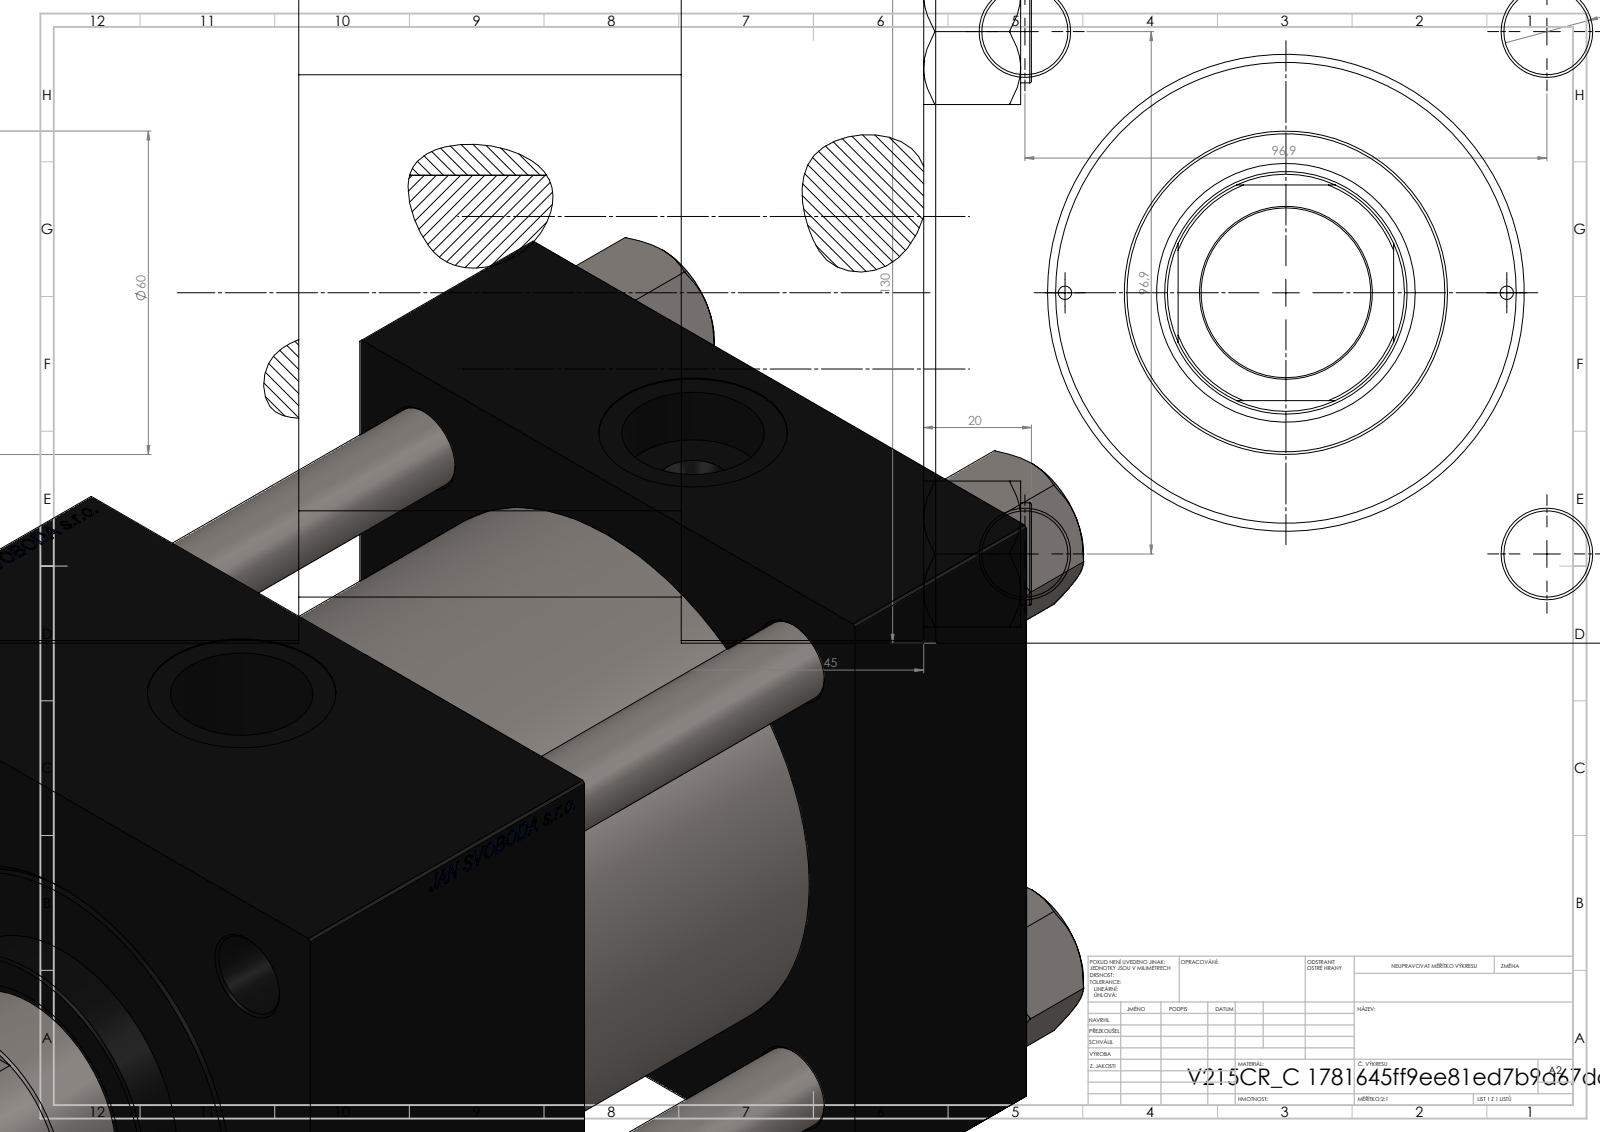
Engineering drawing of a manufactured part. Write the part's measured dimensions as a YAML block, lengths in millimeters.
part_name: "V215CR_C_Body; NUT_M5_C; V215_VC_A; V215CR_C_TYCINKA (+1 more)"
step_written_by: "SolidWorks 2019 (CONFIG_CONTROL_DESIGN)"
units: millimeters
bodies: {solids: 11, faces: 1203, planar: 576, cylindrical: 91, other: 536}
overall_size: [243, 130, 130]
volume: 2425000
surface_area: 326475
round_holes:
  - {diameter: 16, count: 4}
  - {diameter: 2.5, count: 2}
  - {diameter: 7, count: 2}
  - {diameter: 26.44, count: 2}
  - {diameter: 35, count: 2}
  - {diameter: 31.5, count: 1}
  - {diameter: 45, count: 1}
  - {diameter: 48, count: 1}
  - {diameter: 76, count: 1}
  - {diameter: 85.5, count: 1}
  - {diameter: 100, count: 1}
round_bosses_or_shafts:
  - {diameter: 19, count: 4}
  - {diameter: 106, count: 1}
  - {diameter: 60, count: 1}
partial_cylinders:
  - {radius: 22, count: 1}
face_to_face_distances: [130, 45, 188, 143, 116, 71, 72, 20, 96, 51]
hole_center_spacings: [49.02, 68.52, 96.9, 101.73, 41, 137.04, 82, 118.5]
